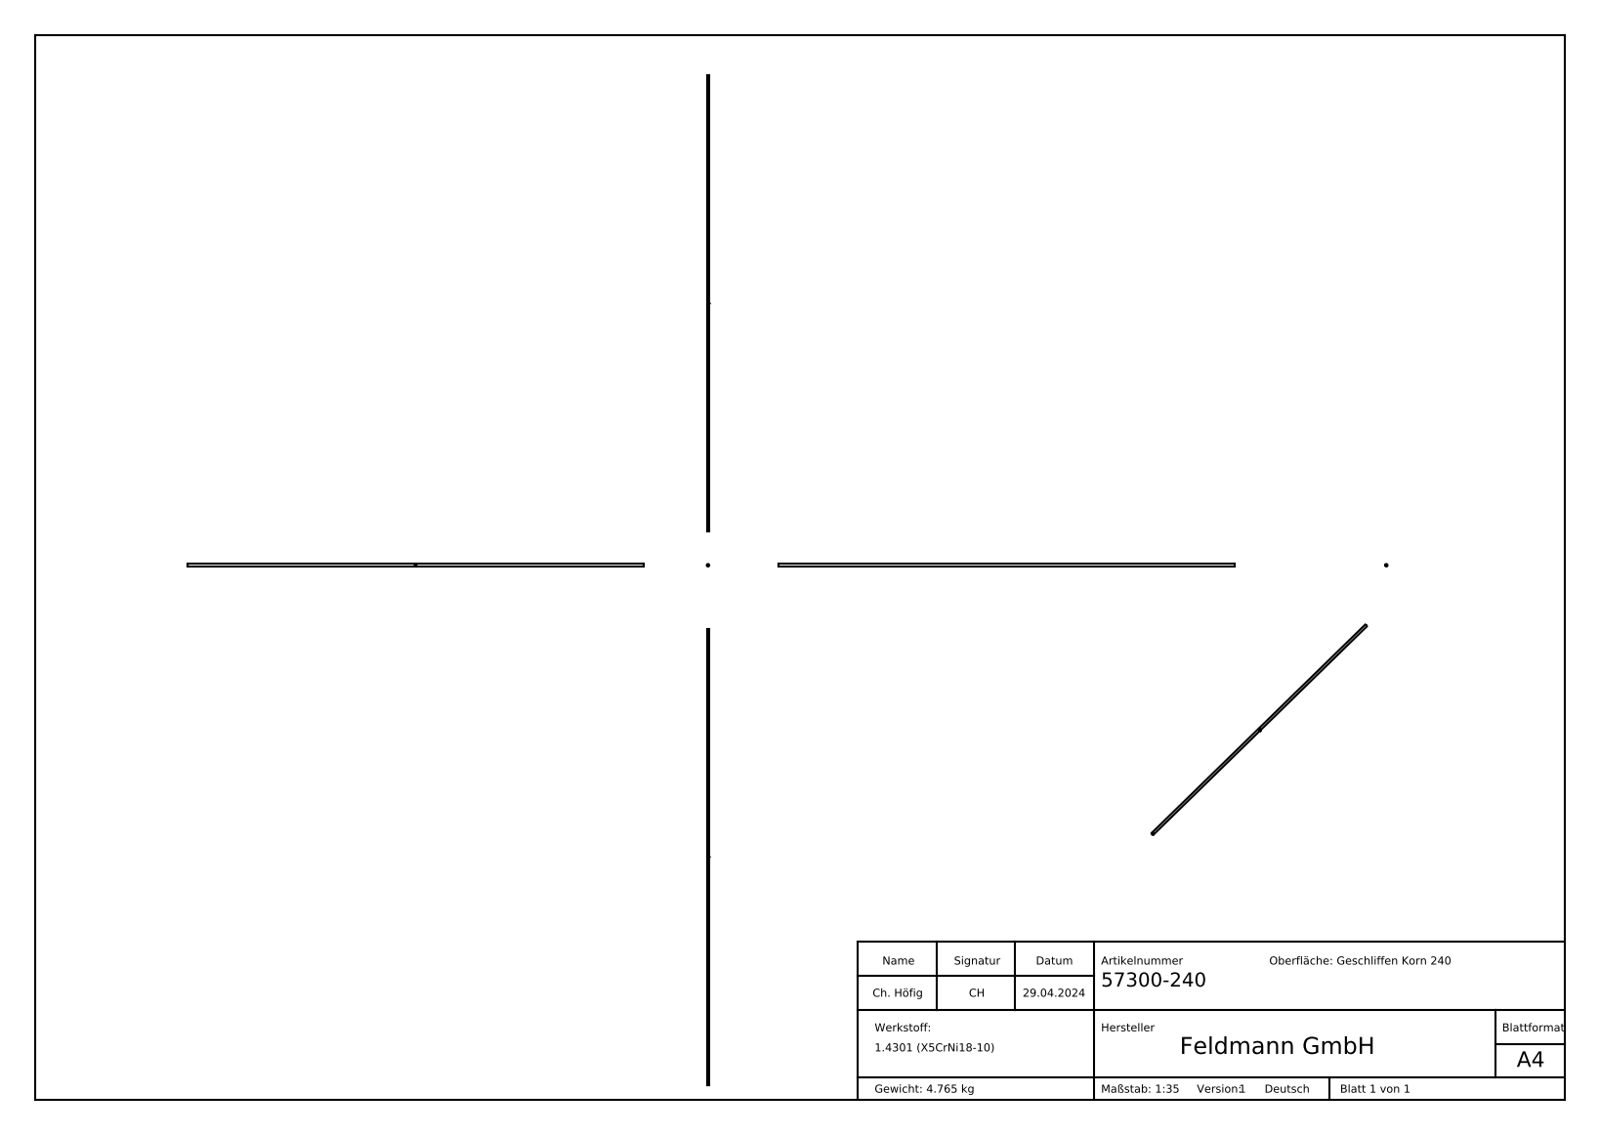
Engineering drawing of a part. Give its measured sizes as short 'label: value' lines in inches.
name: 57300-240
written by: SolidWorks 2018 (CONFIG_CONTROL_DESIGN)
unit: in
bodies: 1 solid, 273 faces (108 planar, 32 cylindrical, 133 other)
size: 118.11 × 0.63 × 0.63
volume: 36.81 in³; area: 234.4 in²
bosses: 1× ⌀0.63
rounds: 1× R0.311
face distances: 118.11, 0.048, 0.08, 0.125, 0.095, 0.03, 0.044, 0.05, 0.033, 0.076
